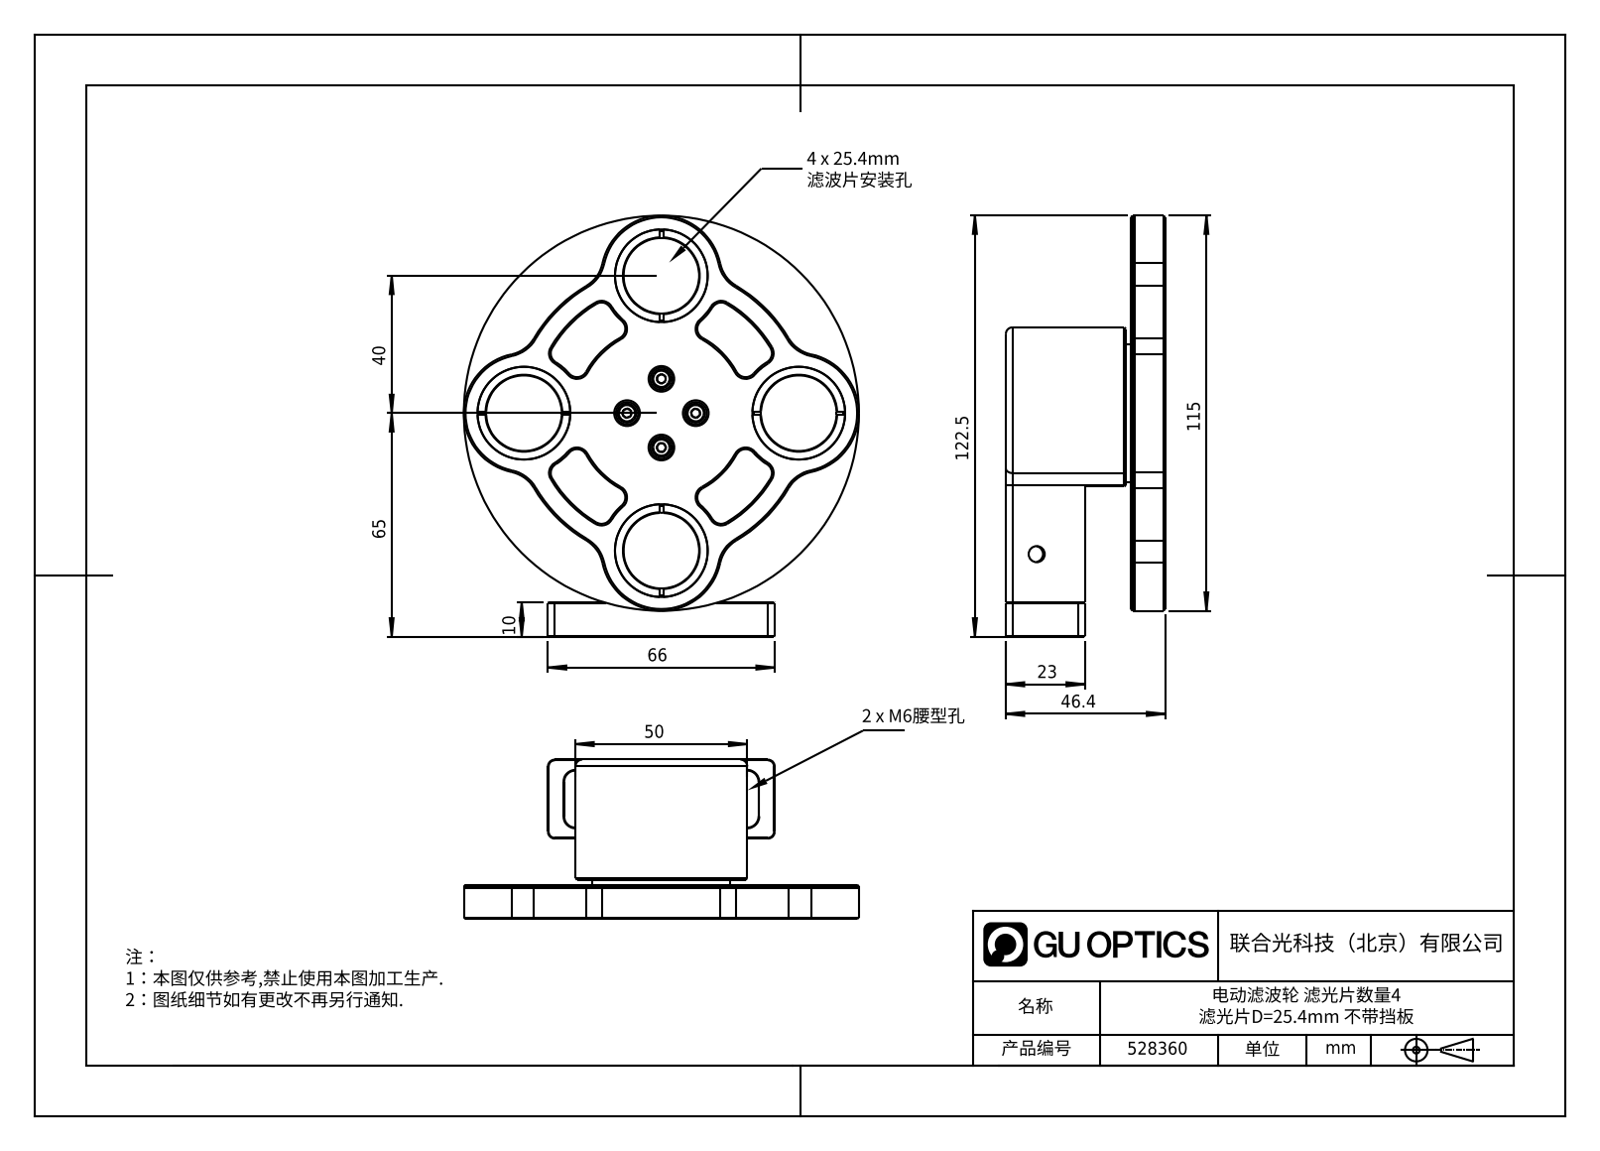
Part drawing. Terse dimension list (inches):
name: 528360
written by: SolidWorks 2020 (CONFIG_CONTROL_DESIGN)
unit: in
bodies: 0 solids, 463 faces (234 planar, 114 cylindrical, 115 other)
size: 4.823 × 4.528 × 1.827
holes: 4× ⌀0.315, 1× ⌀0.185, 1× ⌀1.969, 1× ⌀4.528
bosses: 4× ⌀0.906, 4× ⌀0.866, 4× ⌀0.256, 4× ⌀0.217, 4× ⌀0.205, 3× ⌀0.276, 2× ⌀0.138, 1× ⌀1.575
rounds: 21× R0.012, 16× R0.118, 8× R0.394, 6× R0.079, 4× R0.13, 4× R0.689, 2× R0.197, 1× R1.457
face distances: 0.039, 0.394, 0.354, 1.433, 1.472, 1.827, 1.669, 0.236, 0.197, 0.157
hole spacings: 0.472, 1.063, 1.163
